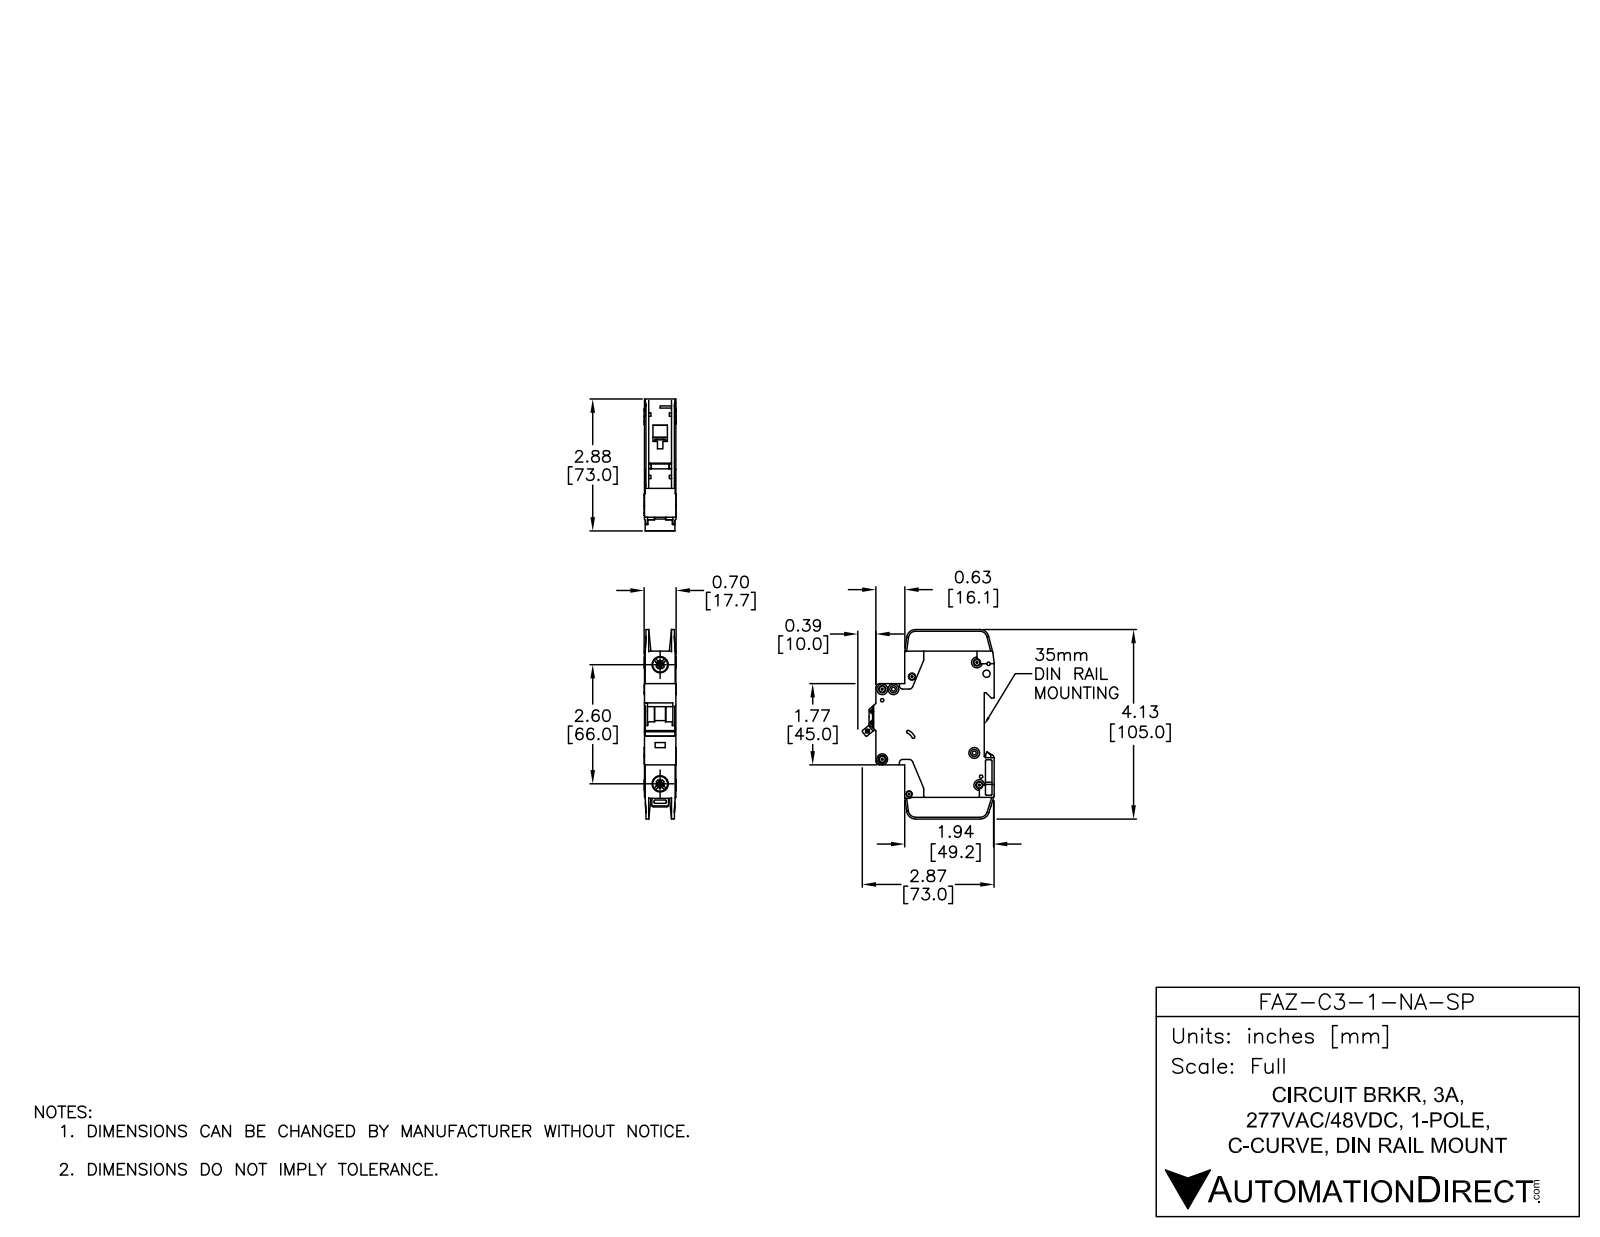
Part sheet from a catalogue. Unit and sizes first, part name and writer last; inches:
Units: inches
Overall size (bounding box): 4.134 × 2.876 × 0.697
Round holes (diameter × count): ⌀0.142 ×7, ⌀0.043 ×2, ⌀0.059 ×2, ⌀0.157 ×2, ⌀0.281 ×2, ⌀0.323 ×2, ⌀0.075 ×1, ⌀0.085 ×1, ⌀0.087 ×1, ⌀0.1 ×1, ⌀0.13 ×1, ⌀0.134 ×1
Round bosses / shafts (diameter × count): ⌀0.236 ×7, ⌀0.098 ×1
Partial cylindrical surfaces — rounded edges, fillets, slot ends (radius × count): R0.01 ×29, R0.02 ×18, R0.039 ×10, R0.079 ×10, R0.197 ×5, R0.157 ×4, R0.071 ×3, R0.008 ×2
Main face-to-face distances: 0.689, 0.593, 0.028, 0.096, 0.069, 0.62, 0.524, 0.551, 0.496, 0.079
Hole centre spacings: 0.244, 0.204, 0.24, 0.322, 0.337, 0.343, 0.437, 0.49
Volume: 4.741 in³ · Surface area: 38.35 in²
Bodies: 3 solids, 784 faces (409 planar, 263 cylindrical, 112 other)
Part name (STEP PRODUCT): FAZ-C3-1-NA-SP
STEP written by: SolidWorks 2014 (AUTOMOTIVE_DESIGN)
